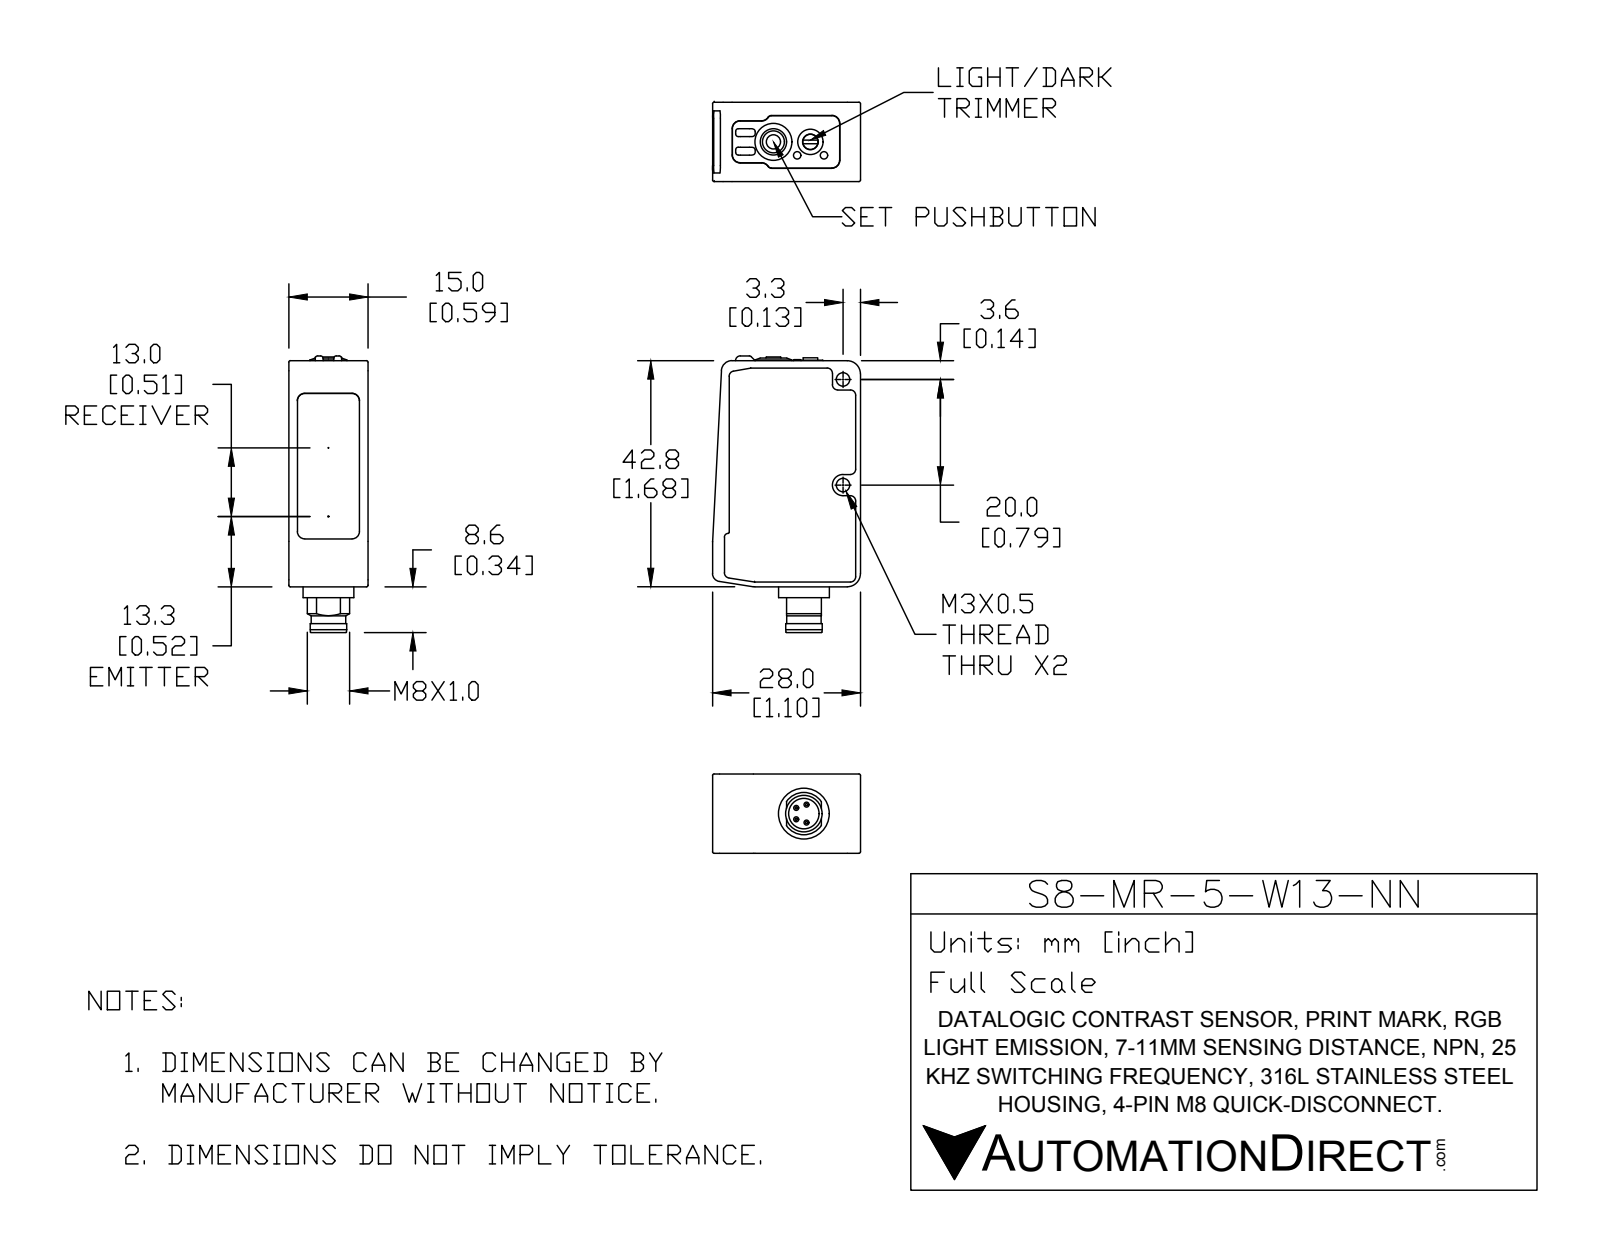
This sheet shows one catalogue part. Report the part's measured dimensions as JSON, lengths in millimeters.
{"part_name": "S8-MR-5-W13-NN", "step_written_by": "SolidWorks 2016 (AUTOMOTIVE_DESIGN)", "units": "millimeters", "bodies": {"solids": 9, "faces": 250, "planar": 66, "cylindrical": 107, "other": 77}, "overall_size": [52.35, 28, 15], "volume_mm3": 17518, "surface_area_mm2": 5614, "round_holes": [[2.54, 2], [1.4, 1], [2.95, 1], [5.77, 1]], "round_bosses_or_shafts": [[0.95, 4], [9.6, 1], [7, 1], [6.9, 1], [6.52, 1], [2.85, 1], [2.7, 1], [1.4, 1]], "partial_cylinders_radius": [[0.3, 23], [0.5, 9], [1.5, 7], [0.2, 6], [1.4, 4], [1.46, 4], [0.71, 2], [0.75, 2]], "face_to_face_distances": [15, 41.7, 1.1, 42.8, 28, 14, 5.25, 46.95, 48.05, 2.5], "hole_center_spacings": [1.23, 3.63, 4.59, 13, 20]}
